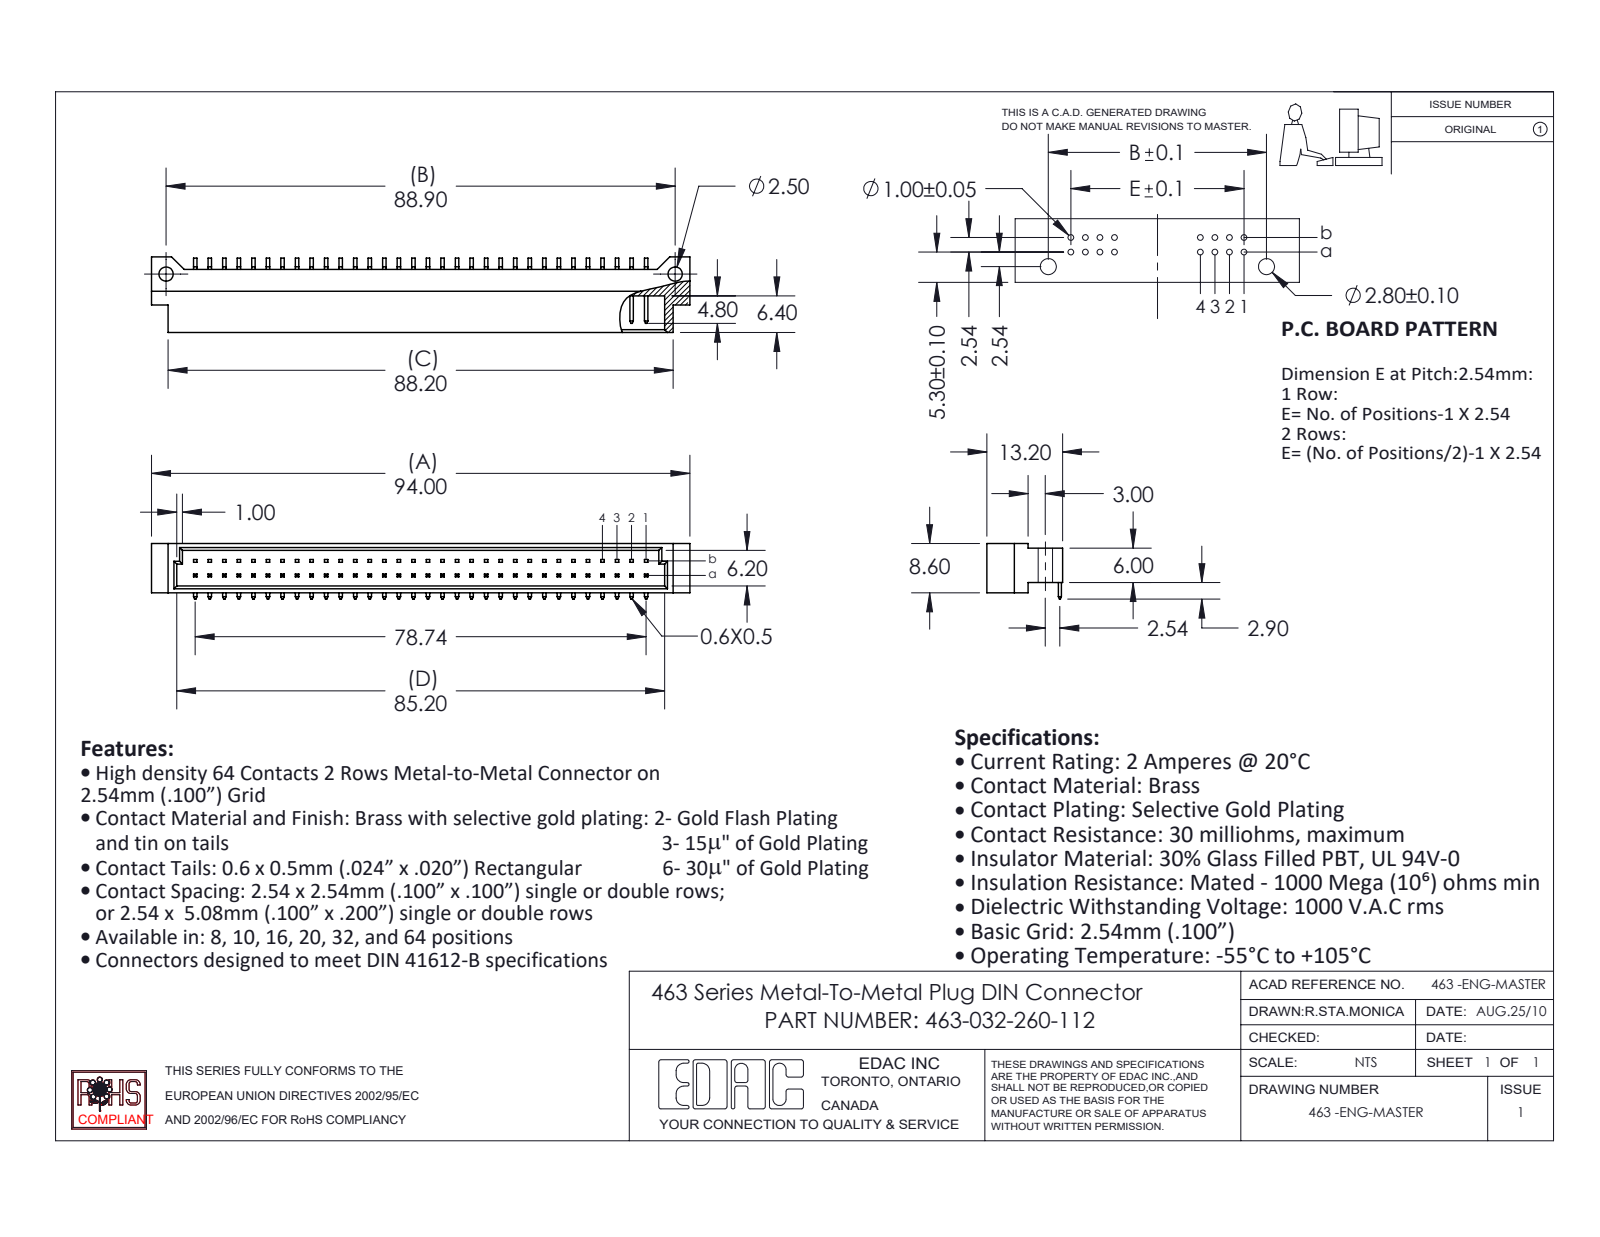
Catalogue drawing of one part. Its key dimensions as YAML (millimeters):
part_name: "463-290-1; 463 Part_64; 463-032-260-112"
step_written_by: "SolidWorks 2020 (CONFIG_CONTROL_DESIGN)"
units: millimeters
bodies: {solids: 33, faces: 871, planar: 803, cylindrical: 68, other: 0}
overall_size: [94, 13.2, 9.7]
volume: 4463
surface_area: 6700
round_holes:
  - {diameter: 2.5, count: 2}
partial_cylinders:
  - {radius: 1.02, count: 1}
  - {radius: 1.52, count: 1}
face_to_face_distances: [1.2, 7.4, 8.6, 0.8, 6.2, 4.6, 6, 6.8, 0.5, 5.6]
hole_center_spacings: [88.9]
